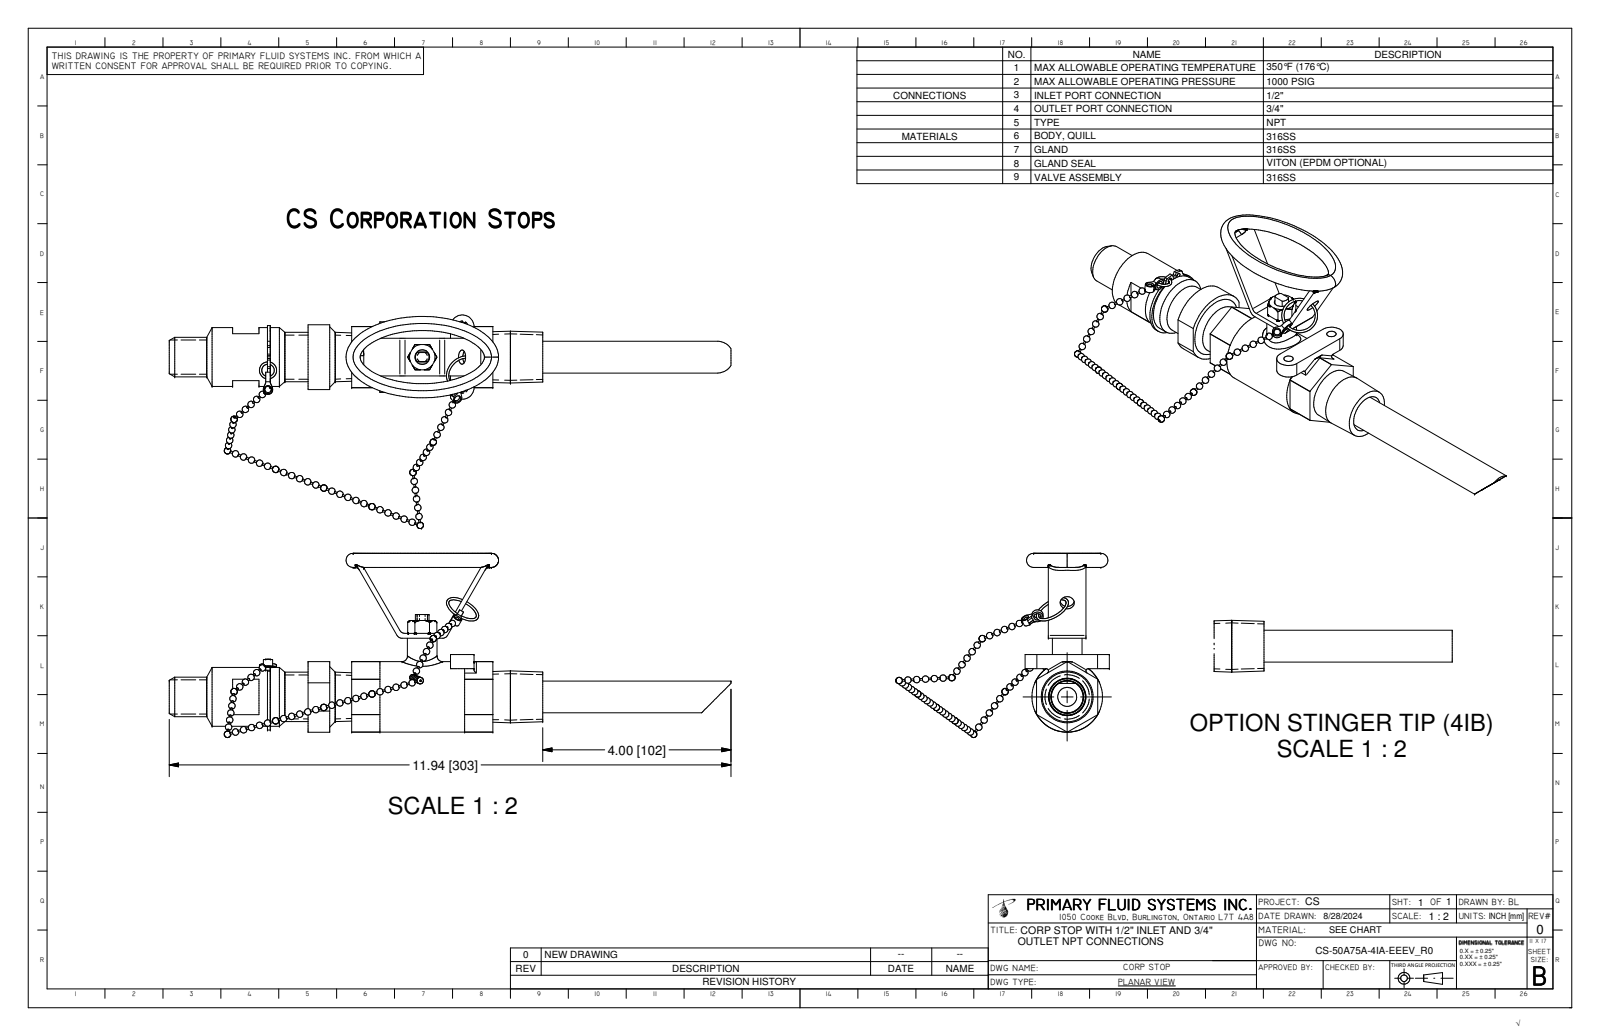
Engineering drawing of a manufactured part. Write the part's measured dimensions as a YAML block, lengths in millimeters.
step_written_by: "Autodesk Inventor 2025 (CONFIG_CONTROL_DESIGN)"
units: millimeters
bodies: {solids: 21, faces: 349, planar: 139, cylindrical: 114, other: 96}
overall_size: [303.2, 115.2, 99.4]
volume: 174500
surface_area: 77480
round_holes:
  - {diameter: 2.5, count: 2}
  - {diameter: 3.8, count: 2}
  - {diameter: 4, count: 2}
  - {diameter: 5.1, count: 2}
  - {diameter: 7.6, count: 1}
  - {diameter: 8, count: 1}
  - {diameter: 10.2, count: 1}
  - {diameter: 10.7, count: 1}
  - {diameter: 17.7, count: 1}
  - {diameter: 20, count: 1}
  - {diameter: 20.1, count: 1}
  - {diameter: 20.4, count: 1}
round_bosses_or_shafts:
  - {diameter: 0.9, count: 9}
  - {diameter: 6, count: 2}
  - {diameter: 38, count: 1}
  - {diameter: 34.1, count: 1}
  - {diameter: 31.8, count: 1}
  - {diameter: 29, count: 1}
  - {diameter: 21.3, count: 1}
  - {diameter: 17.1, count: 1}
partial_cylinders:
  - {radius: 3.2, count: 8}
  - {radius: 1.3, count: 6}
  - {radius: 1.4, count: 2}
  - {radius: 2.5, count: 2}
  - {radius: 5, count: 2}
  - {radius: 6.4, count: 2}
  - {radius: 3.7, count: 1}
  - {radius: 19.1, count: 1}
face_to_face_distances: [33, 6.4, 2.6, 7.6, 2.6, 23.5, 26.7, 76.2, 99.7, 1.3]
hole_center_spacings: [16.7, 27.1, 6.4, 8, 14.4, 18, 20.7, 32.8]
